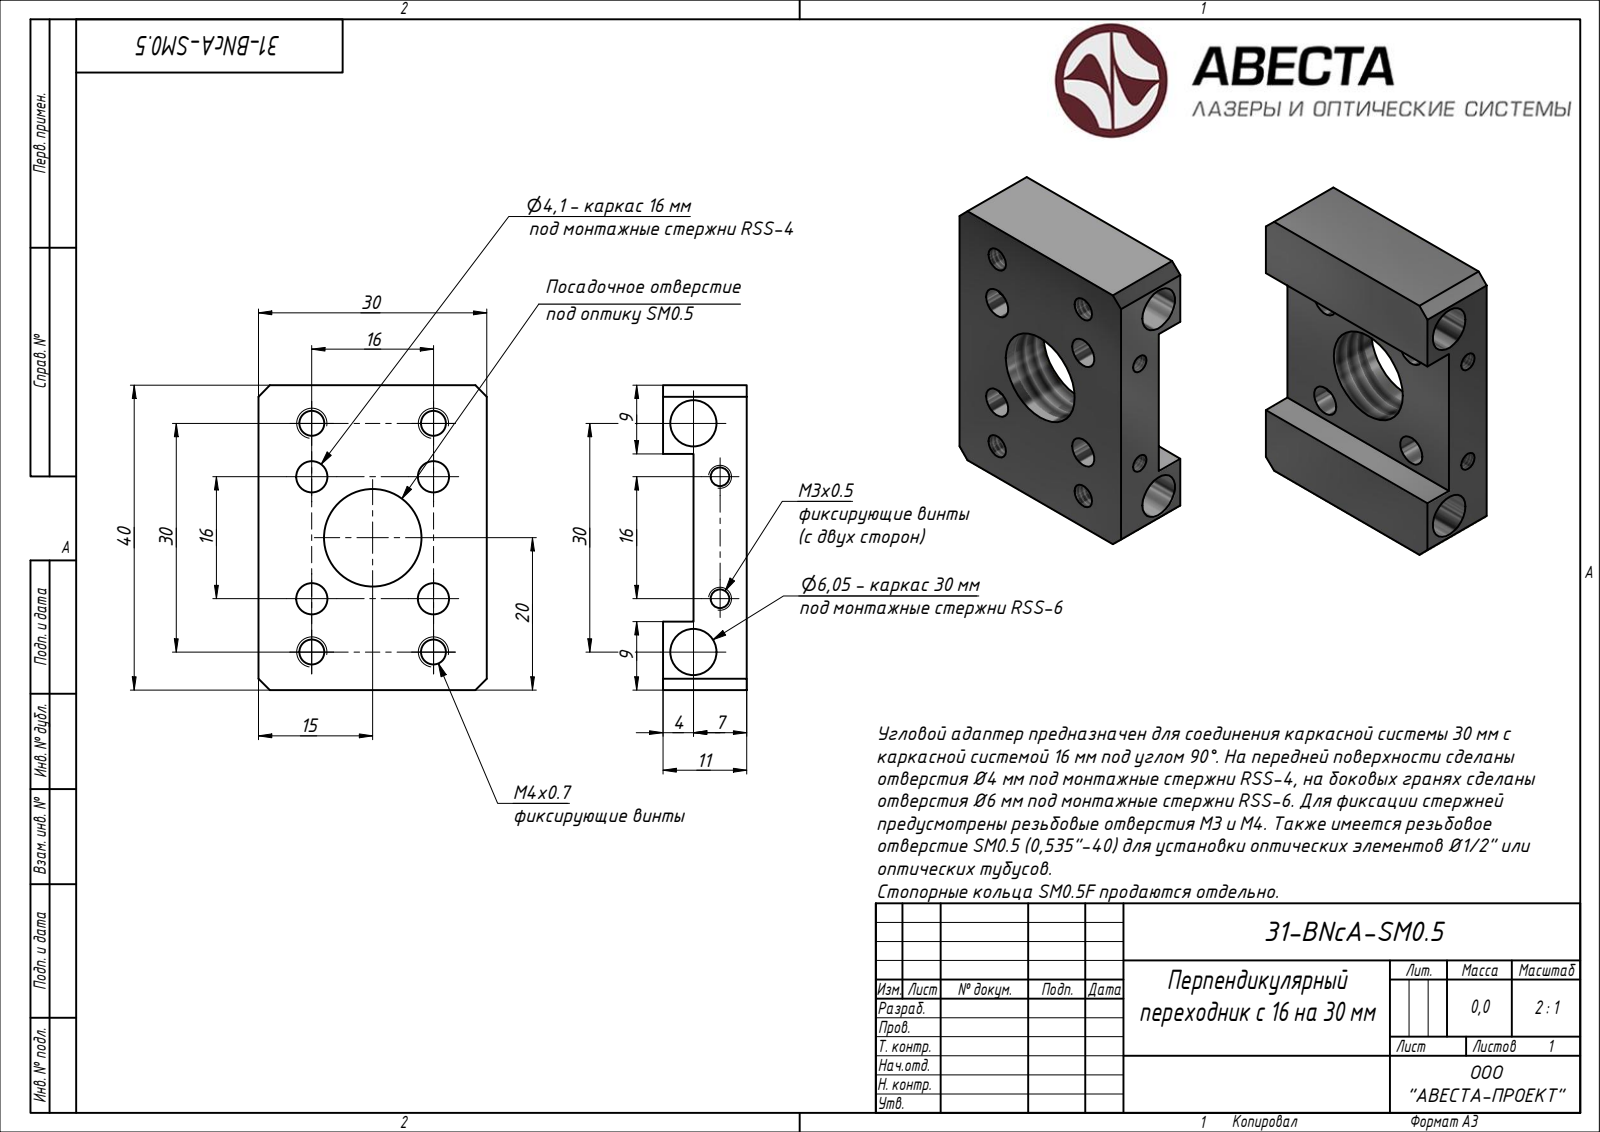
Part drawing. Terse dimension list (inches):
name: 31-BNcA-SM0.5
written by: Autodesk Inventor 2020 (AUTOMOTIVE_DESIGN)
unit: in
bodies: 1 solid, 29 faces (14 planar, 15 cylindrical, 0 other)
size: 1.575 × 1.181 × 0.433
volume: 0.445 in³; area: 8.502 in²
holes: 4× ⌀0.128, 4× ⌀0.161, 2× ⌀0.097, 2× ⌀0.238, 1× ⌀0.503
face distances: 0.433, 0.157, 0.276, 1.575, 1.181, 0.354, 1.22, 0.866, 1.865
hole spacings: 0.63, 0.276, 0.445, 0.669, 0.687, 0.906, 1.103, 1.181
